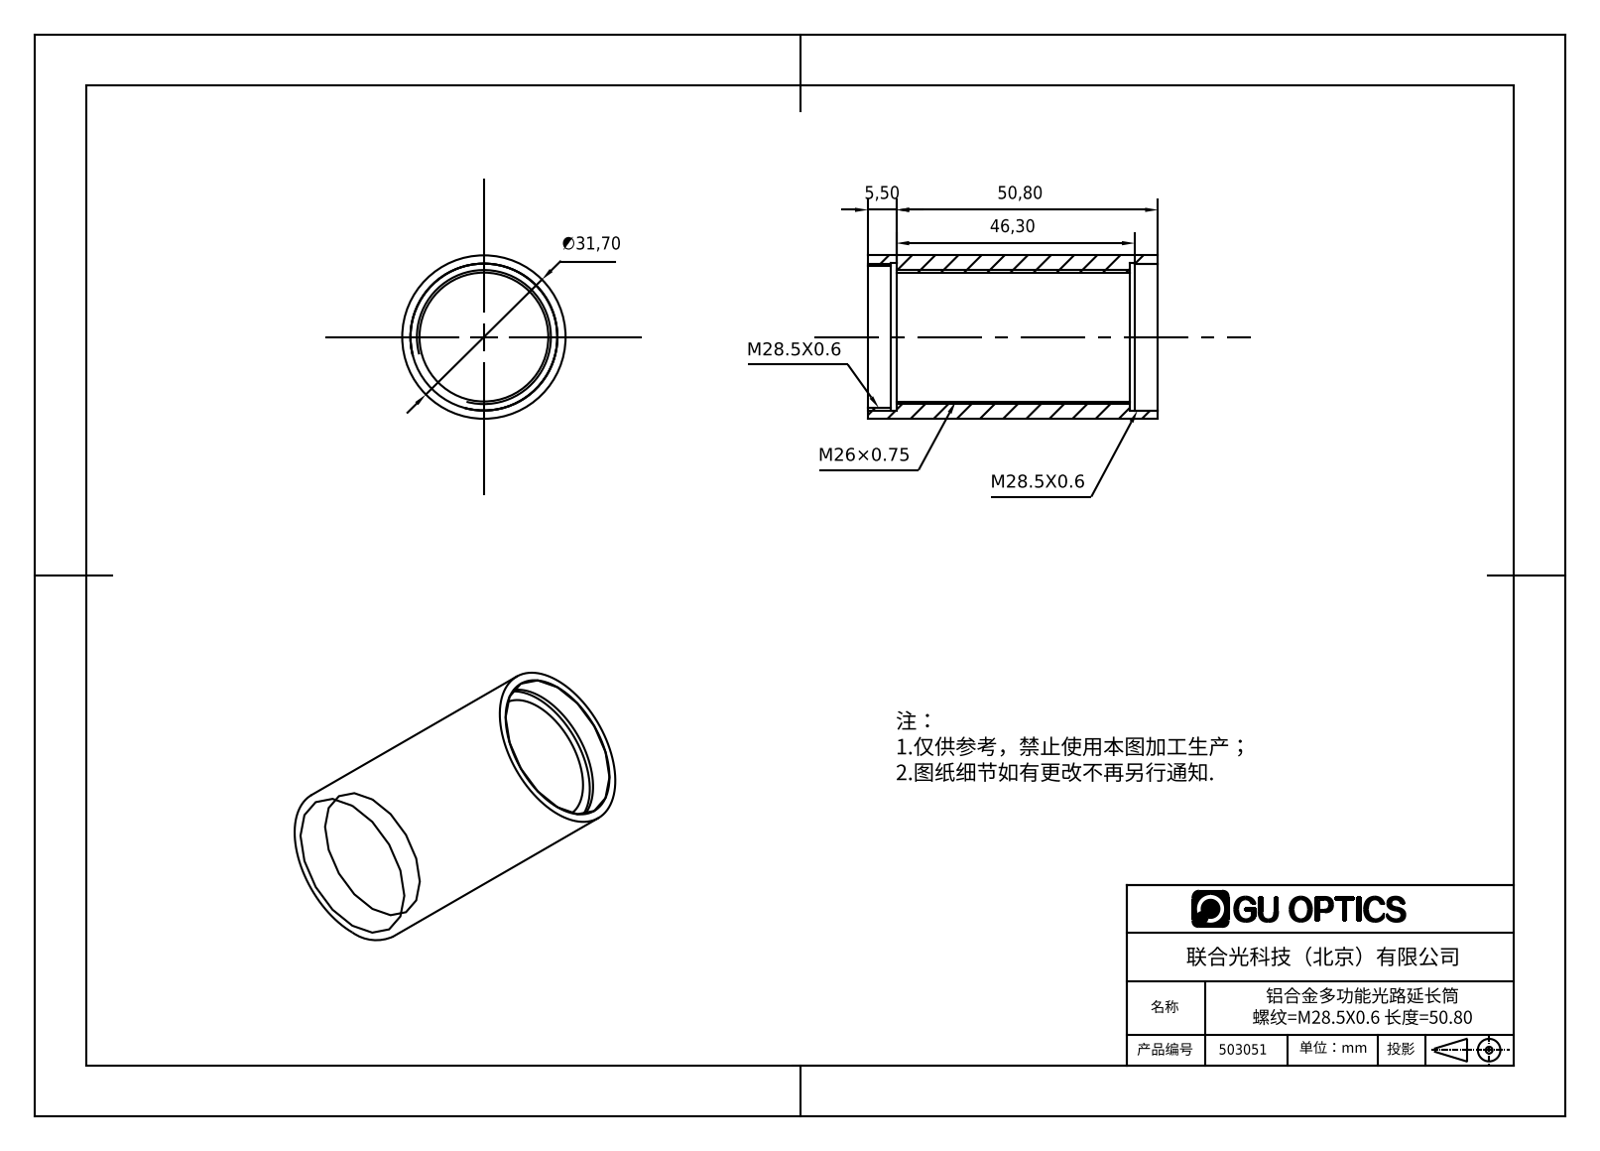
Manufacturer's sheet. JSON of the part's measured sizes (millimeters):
{"part_name": "503051", "step_written_by": "SolidWorks 2016 (AUTOMOTIVE_DESIGN)", "units": "millimeters", "bodies": {"solids": 1, "faces": 18, "planar": 6, "cylindrical": 12, "other": 0}, "overall_size": [56.3, 31.7, 31.7], "volume_mm3": 15360, "surface_area_mm2": 10857, "round_holes": [[25, 1], [27.5, 1], [28.5, 1], [28.7, 1]], "round_bosses_or_shafts": [[31.7, 1]], "face_to_face_distances": [5.5, 50.8, 45.3, 56.3, 4.5, 51.8, 1, 46.3, 47.3]}
